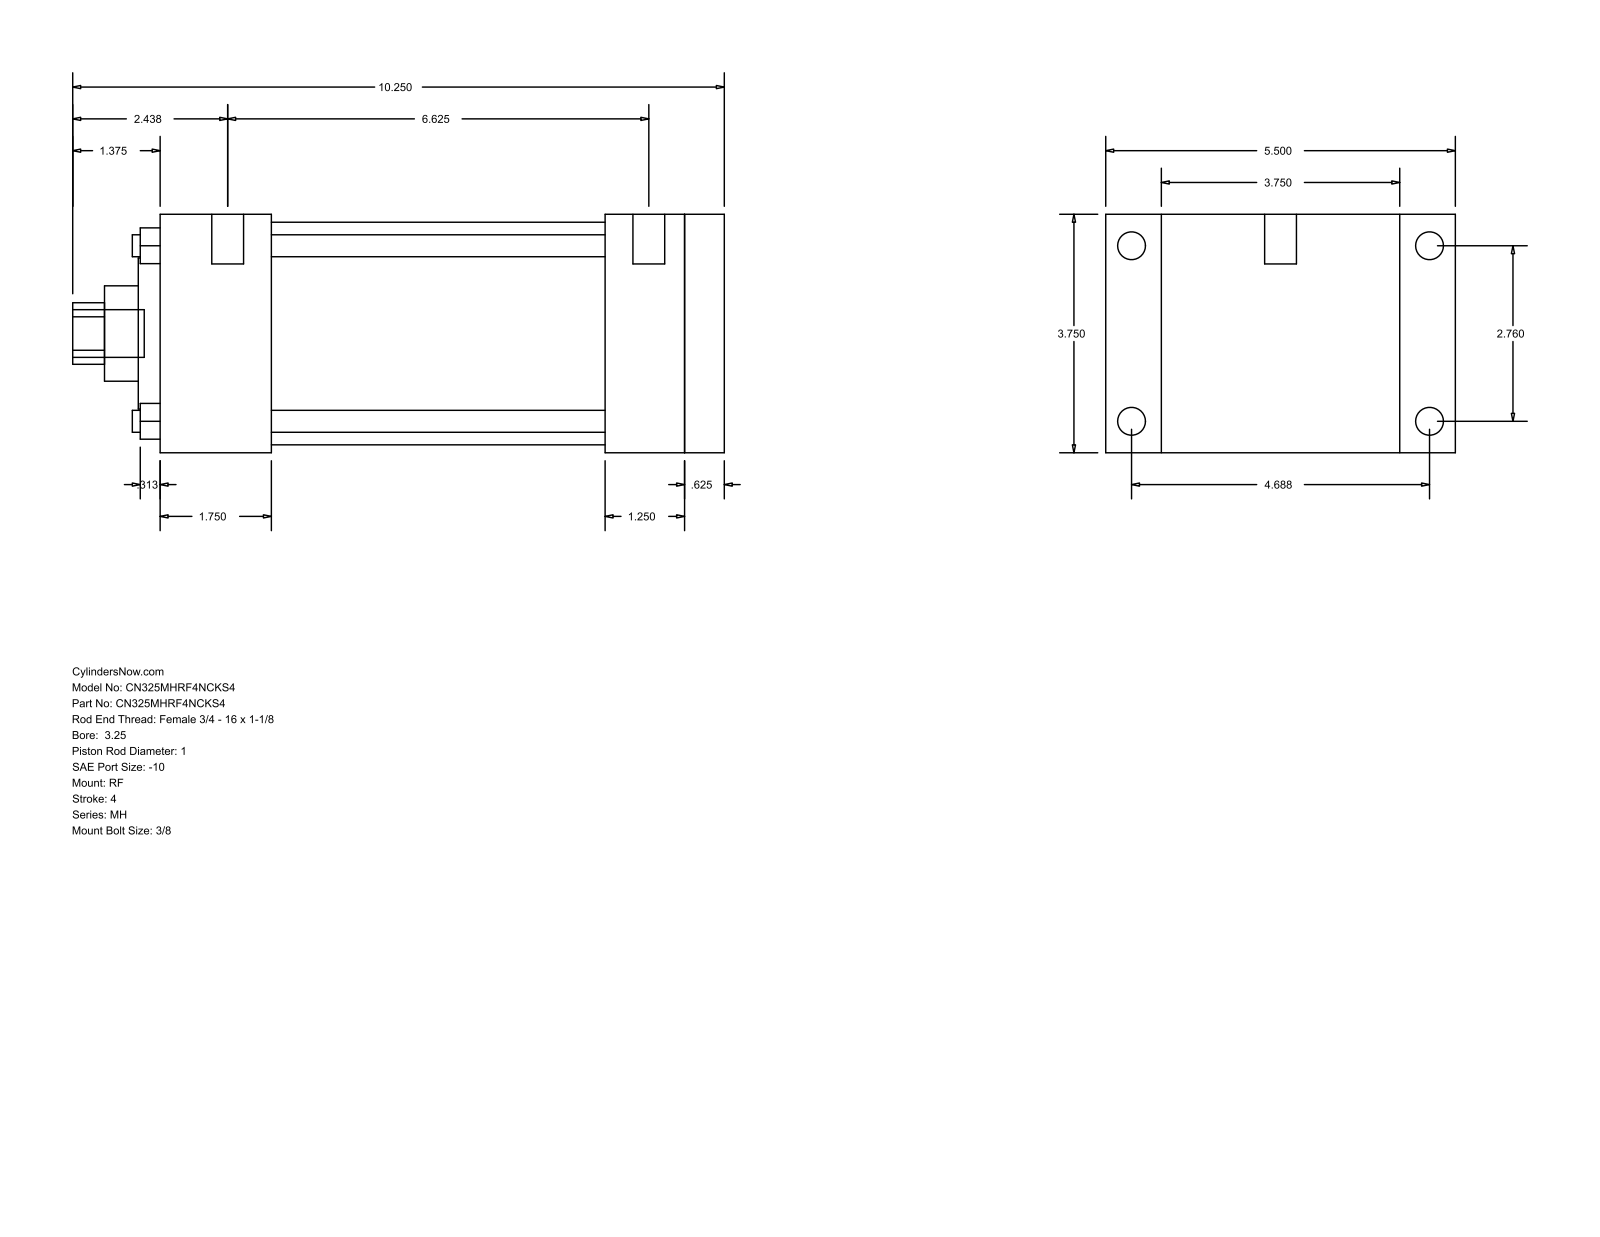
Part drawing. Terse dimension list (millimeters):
name: MH_RF__0325_1
written by: GSSL Pune (CONFIG_CONTROL_DESIGN)
unit: mm
bodies: 0 solids, 94 faces (65 planar, 29 cylindrical, 0 other)
size: 260.35 × 139.7 × 95.25
holes: 4× ⌀8.76, 1× ⌀25.4, 1× ⌀38.1, 1× ⌀60.33, 1× ⌀88.9
bosses: 4× ⌀11.13, 4× ⌀5.56, 2× ⌀12.7, 1× ⌀19.05
rounds: 1× R12.29
face distances: 95.24, 225.43, 209.55, 15.88, 22.23, 117.47, 44.46, 165.09, 180.97, 177.8
hole spacings: 49.57, 70.1, 99.14
